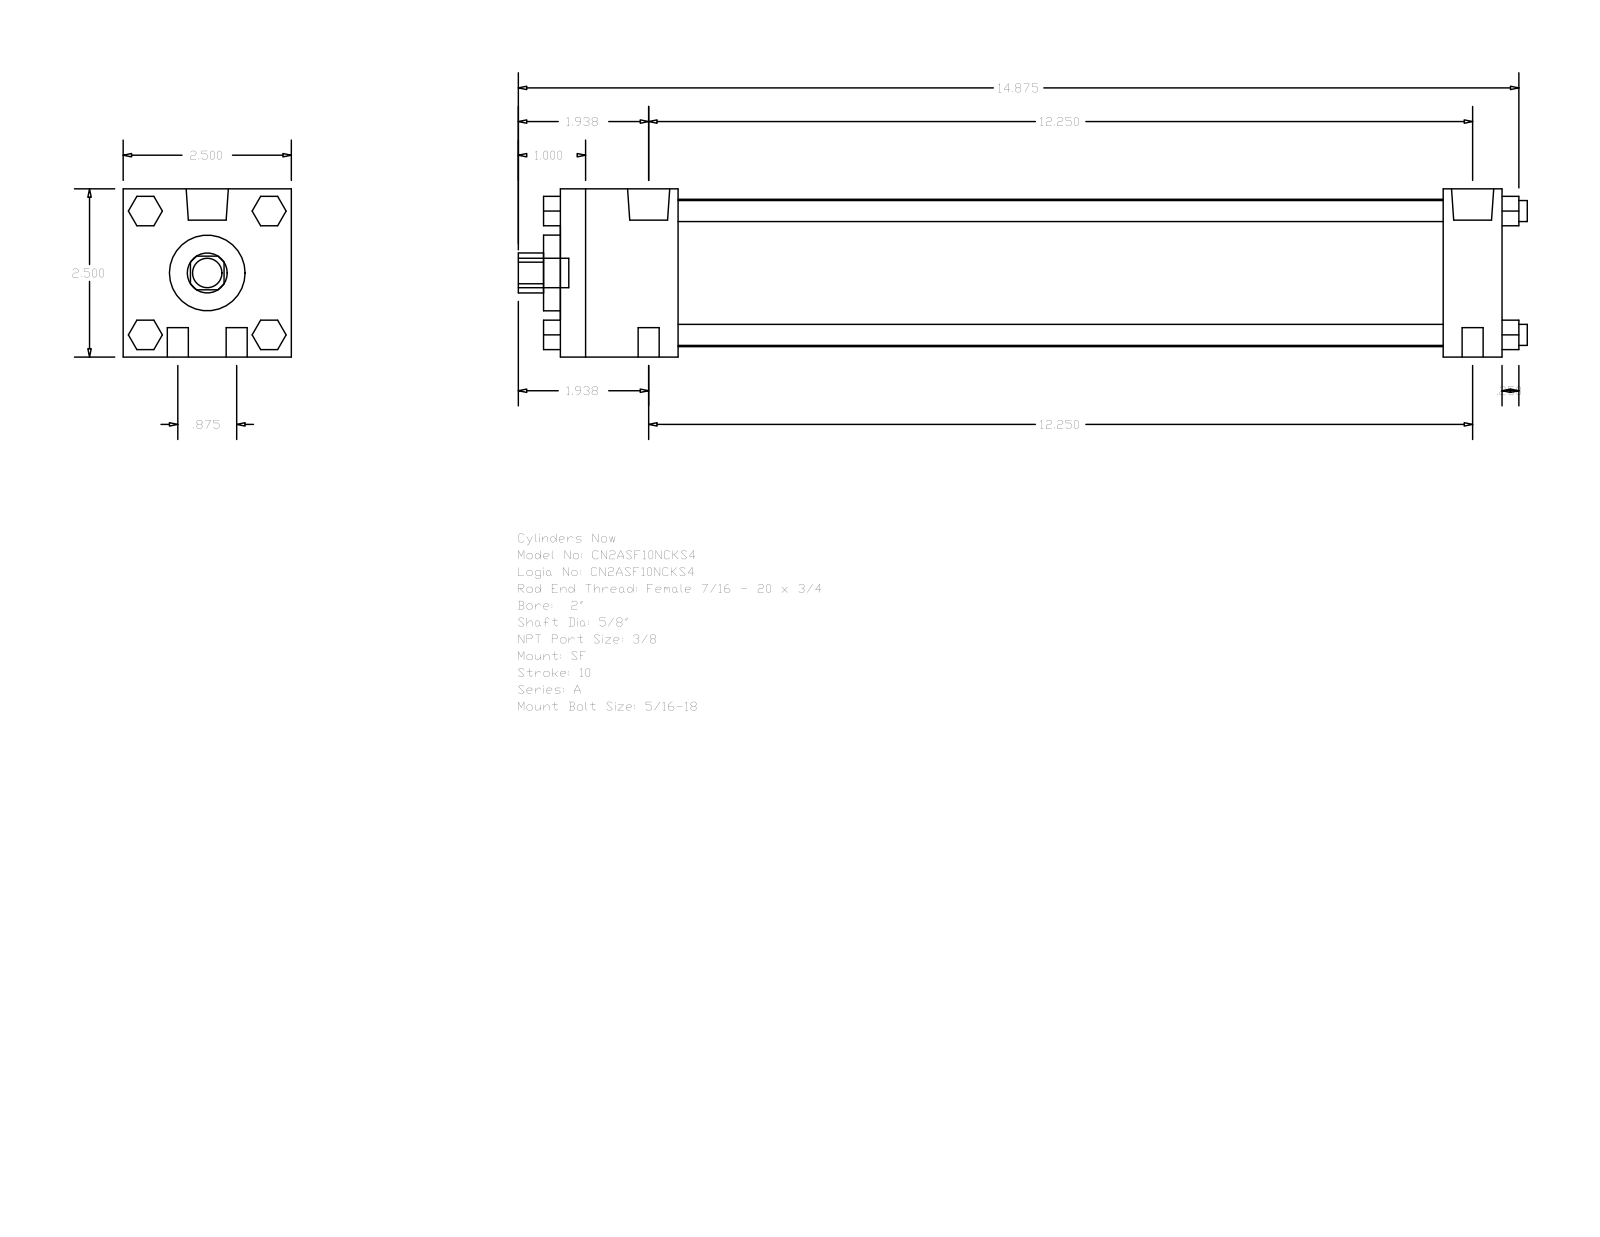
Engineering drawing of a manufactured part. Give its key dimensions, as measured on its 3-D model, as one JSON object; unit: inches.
{"part_name": "A_SF__0200_0.625", "step_written_by": "GSSL Pune (CONFIG_CONTROL_DESIGN)", "units": "inches", "bodies": {"solids": 0, "faces": 124, "planar": 94, "cylindrical": 30, "other": 0}, "overall_size": [15, 2.5, 2.5], "round_holes": [[0.625, 1], [1.125, 1], [2.19, 1]], "round_bosses_or_shafts": [[0.313, 8], [0.627, 2], [0.219, 2], [0.437, 1]], "partial_cylinders_radius": [[0.297, 1]], "face_to_face_distances": [2.5, 14, 13.125, 0.875, 1.75, 11.375, 12.25, 2, 14.25, 0.25]}
